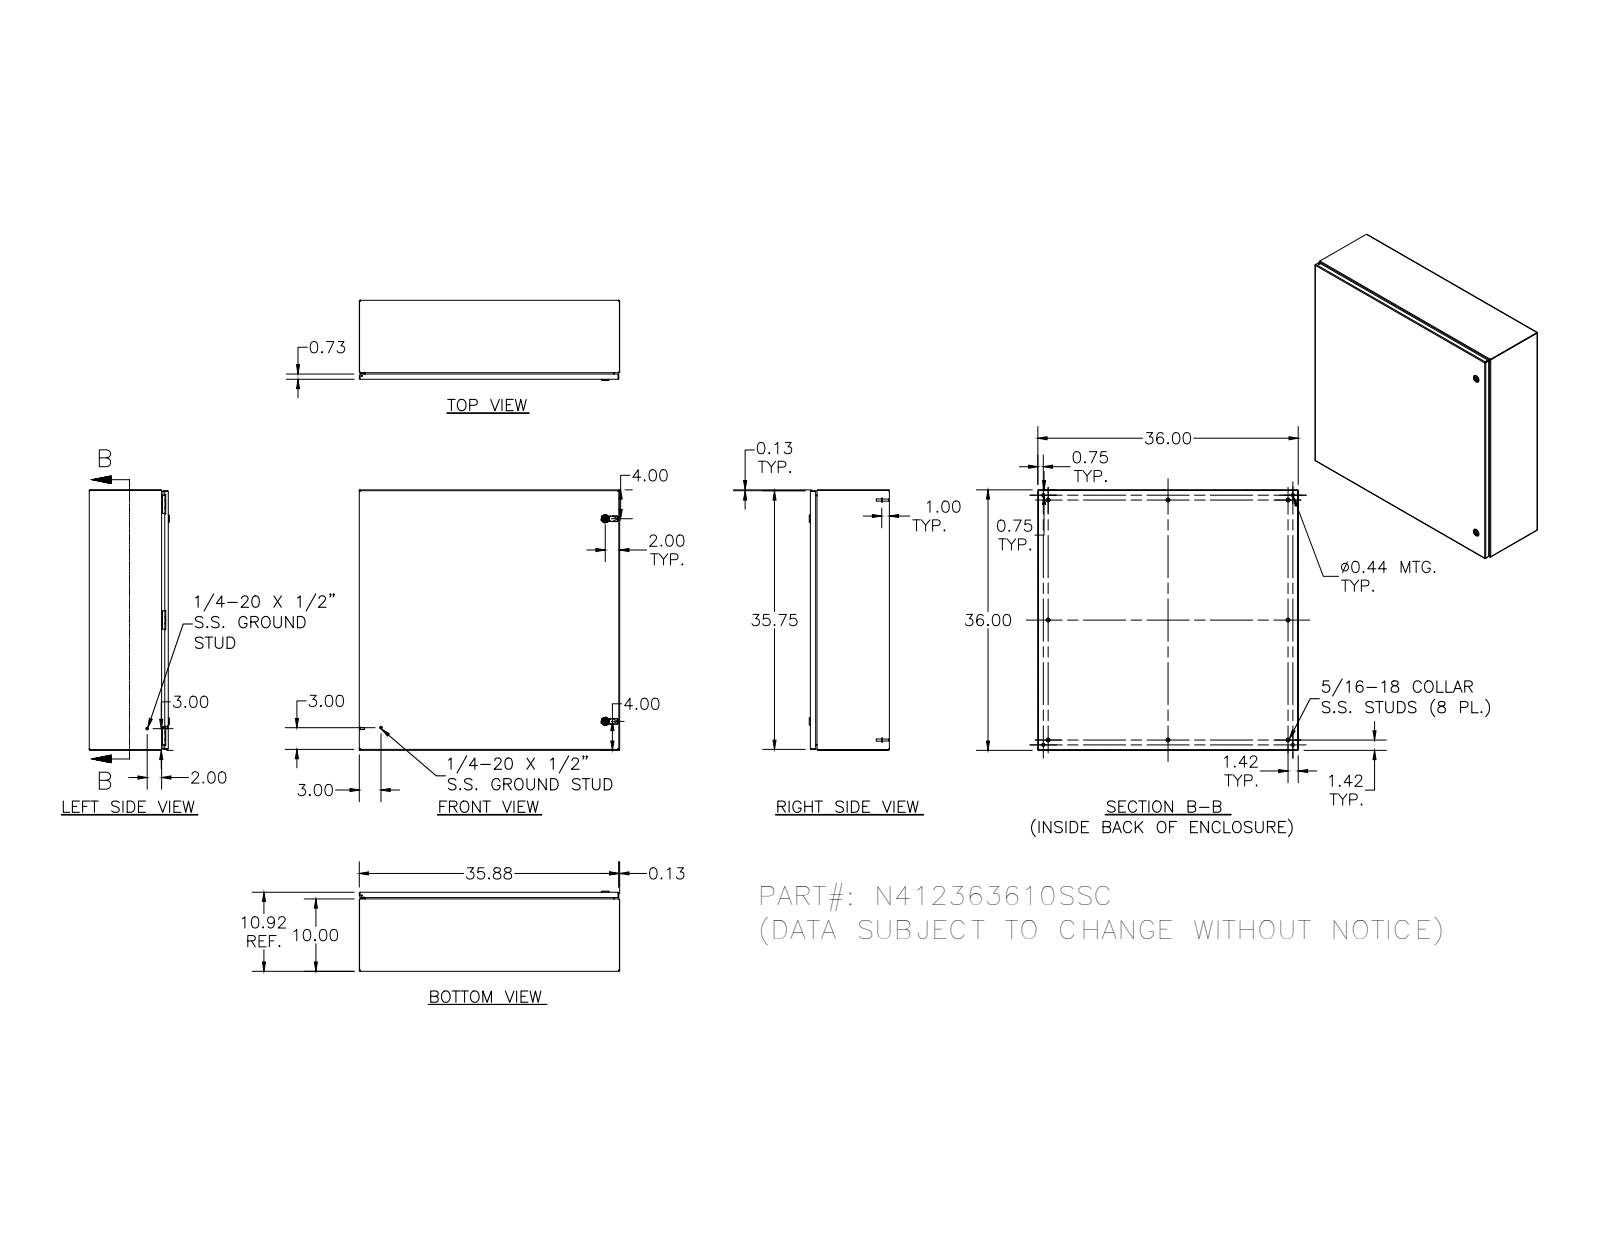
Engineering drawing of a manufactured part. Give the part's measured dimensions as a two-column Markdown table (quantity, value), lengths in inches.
| quantity | value |
| --- | --- |
| part name | N412SSCASSM1PC; N412363610SSCBKP; 388151; N4123636SSCLID (+8 more) |
| STEP written by | Autodesk Inventor 2012 (AUTOMOTIVE_DESIGN) |
| units | inches |
| bodies | 55 solids, 2132 faces (839 planar, 782 cylindrical, 511 other) |
| overall size | 36 × 36 × 11.075 |
| volume | 320.6 in³ |
| surface area | 8 690 in² |
| round holes (diameter × count) | 0.093 × 6, 0.152 × 6, 0.167 × 6, 0.172 × 6, 0.188 × 6, 0.437 × 4, 0.156 × 3, 0.197 × 2, 0.315 × 2, 0.394 × 2, 0.402 × 2, 0.634 × 2 |
| round bosses / shafts (diameter × count) | 0.25 × 14, 0.563 × 8, 0.3 × 8, 0.275 × 8, 0.36 × 6, 0.32 × 6, 0.256 × 6, 0.164 × 6 |
| partial cylindrical surfaces (radius × count) | 0.05 × 38, 0.031 × 34, 0.016 × 26, 0.125 × 21, 0.105 × 20, 0.02 × 15, 0.032 × 12, 0.07 × 8 |
| main face-to-face distances | 0.074, 10.843, 35.926, 10.769, 10.917, 35.852, 36, 9.926, 0.917, 0.739 |
| hole center spacings | 16.004, 32, 15.996, 0.017, 0.66, 15.992, 16, 16.008 |
